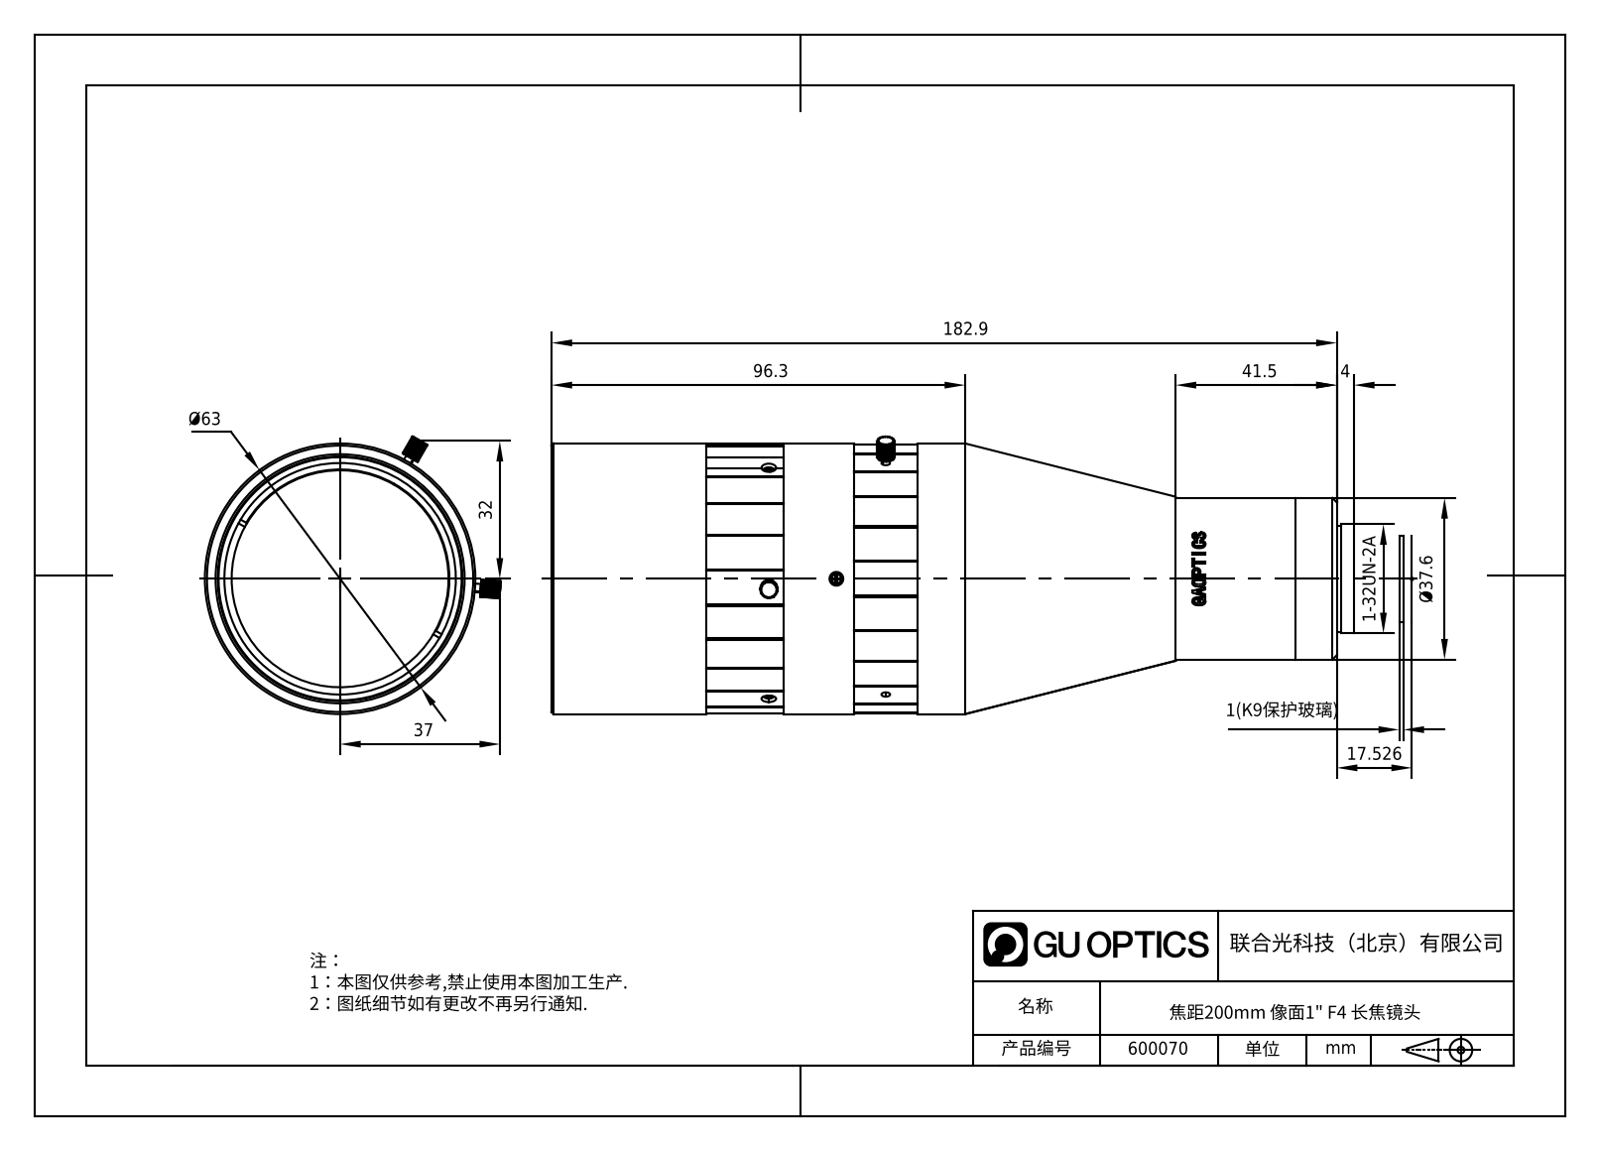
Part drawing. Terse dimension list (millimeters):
name: 600070
written by: SolidWorks 2020 (AUTOMOTIVE_DESIGN)
unit: mm
bodies: 19 solids, 863 faces (315 planar, 330 cylindrical, 218 other)
size: 186.86 × 68.88 × 64.59
volume: 532 397 mm³; area: 111 832 mm²
holes: 9× ⌀2, 3× ⌀1.4, 3× ⌀1.7, 3× ⌀2.1, 3× ⌀3.2, 3× ⌀3.4, 1× ⌀22.3, 1× ⌀30, 1× ⌀35, 1× ⌀40, 1× ⌀41.5, 1× ⌀45.5
bosses: 3× ⌀2.8, 3× ⌀2.5, 2× ⌀1.4, 1× ⌀63, 1× ⌀60, 1× ⌀59.3, 1× ⌀57, 1× ⌀56.8
rounds: 48× R50, 6× R1.5, 2× R2, 1× R1, 1× R18.6, 1× R25.5
face distances: 21, 52.34, 21.9, 74.24, 0.9, 73.34, 31.4, 30.5, 9.5, 42.84
hole spacings: 11.5
